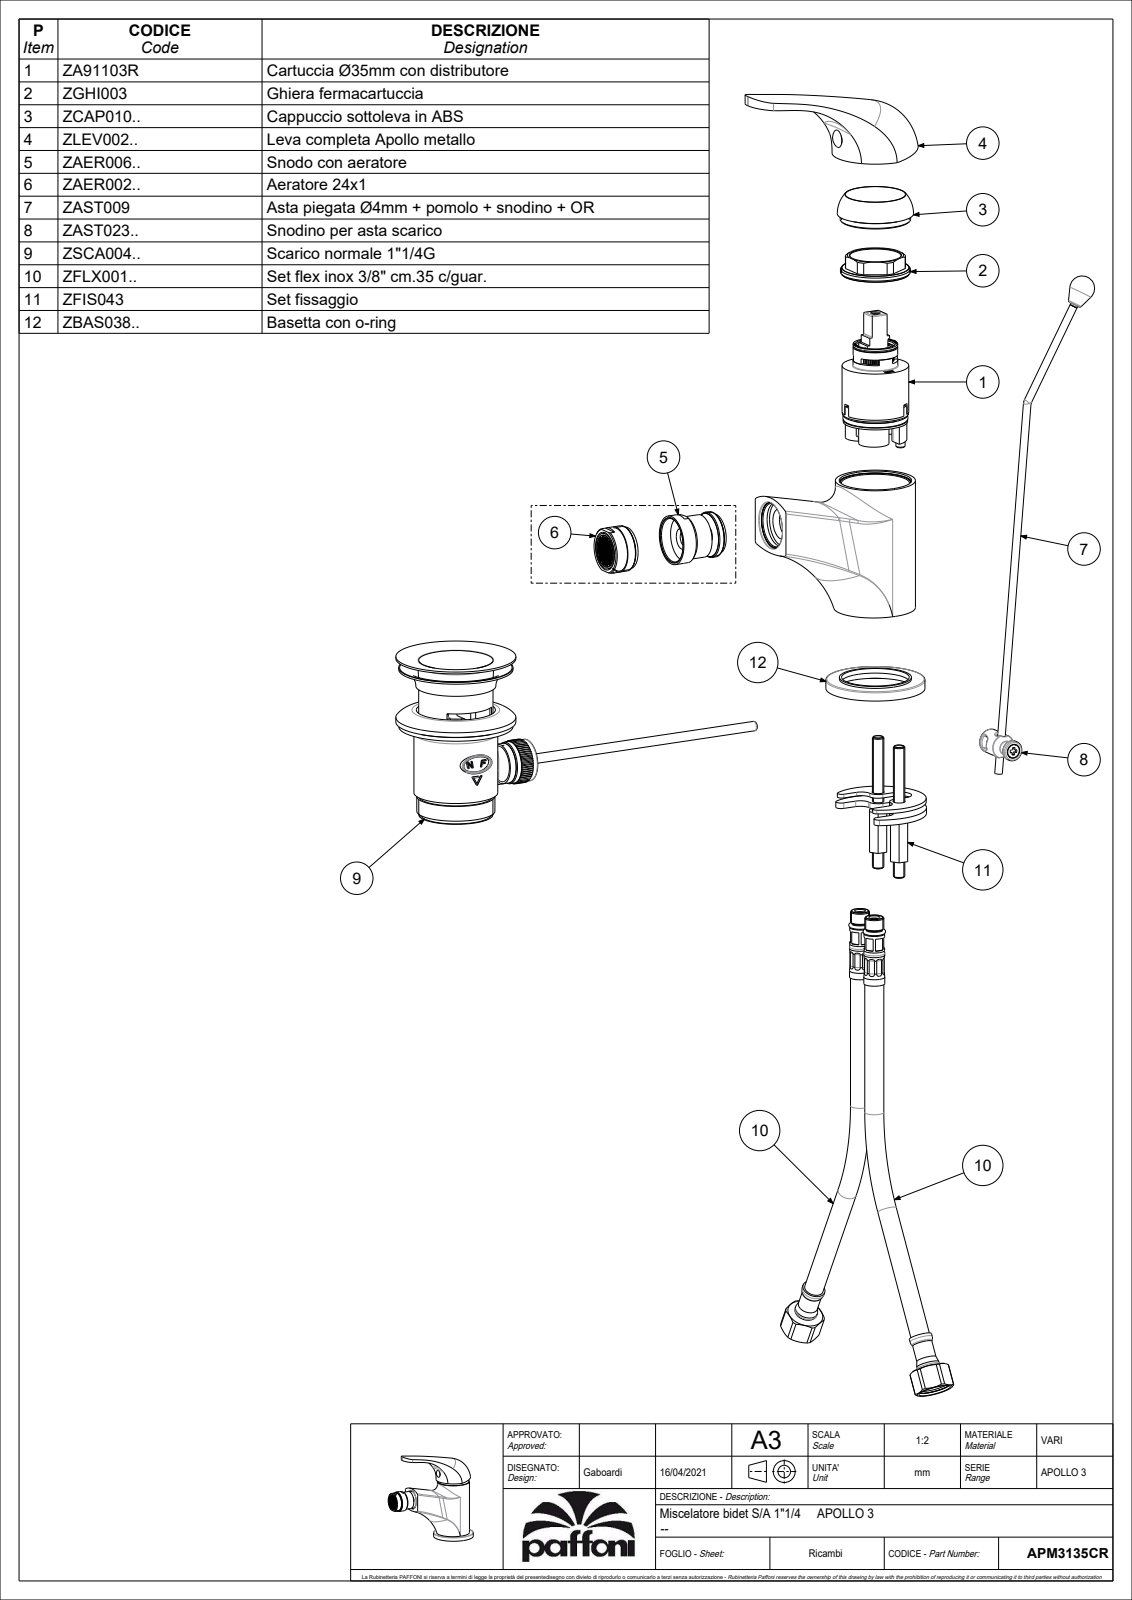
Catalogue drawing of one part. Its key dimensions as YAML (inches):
part_name: "APM3135CR"
step_written_by: "CREO PARAMETRIC BY PTC INC, 2020044 (CONFIG_CONTROL_DESIGN)"
units: inches
bodies: {solids: 3, faces: 2664, planar: 2041, cylindrical: 348, other: 275}
overall_size: [5.381, 4.646, 2.047]
volume: 6.93
surface_area: 124.9
round_holes:
  - {diameter: 0.354, count: 5}
  - {diameter: 0.197, count: 3}
  - {diameter: 0.315, count: 3}
  - {diameter: 0.472, count: 3}
  - {diameter: 0.157, count: 2}
  - {diameter: 0.276, count: 2}
  - {diameter: 0.433, count: 2}
  - {diameter: 0.13, count: 1}
  - {diameter: 0.177, count: 1}
  - {diameter: 0.236, count: 1}
  - {diameter: 0.61, count: 1}
  - {diameter: 0.63, count: 1}
round_bosses_or_shafts:
  - {diameter: 2.047, count: 1}
  - {diameter: 1.677, count: 1}
  - {diameter: 1.654, count: 1}
  - {diameter: 1.488, count: 1}
  - {diameter: 1.37, count: 1}
  - {diameter: 1.331, count: 1}
  - {diameter: 1.268, count: 1}
  - {diameter: 1.24, count: 1}
partial_cylinders:
  - {radius: 0.02, count: 42}
  - {radius: 0.039, count: 12}
  - {radius: 0.006, count: 11}
  - {radius: 0.012, count: 9}
  - {radius: 0.079, count: 8}
  - {radius: 0.197, count: 4}
  - {radius: 0.276, count: 4}
  - {radius: 0.177, count: 2}
face_to_face_distances: [0.118, 0.197, 0.098, 0.472, 0.02, 0.059, 0.067, 1.28, 0.354, 0.138]
hole_center_spacings: [0.535, 0.02, 0.028, 0.044, 0.335, 0.339, 0.355, 0.44]
